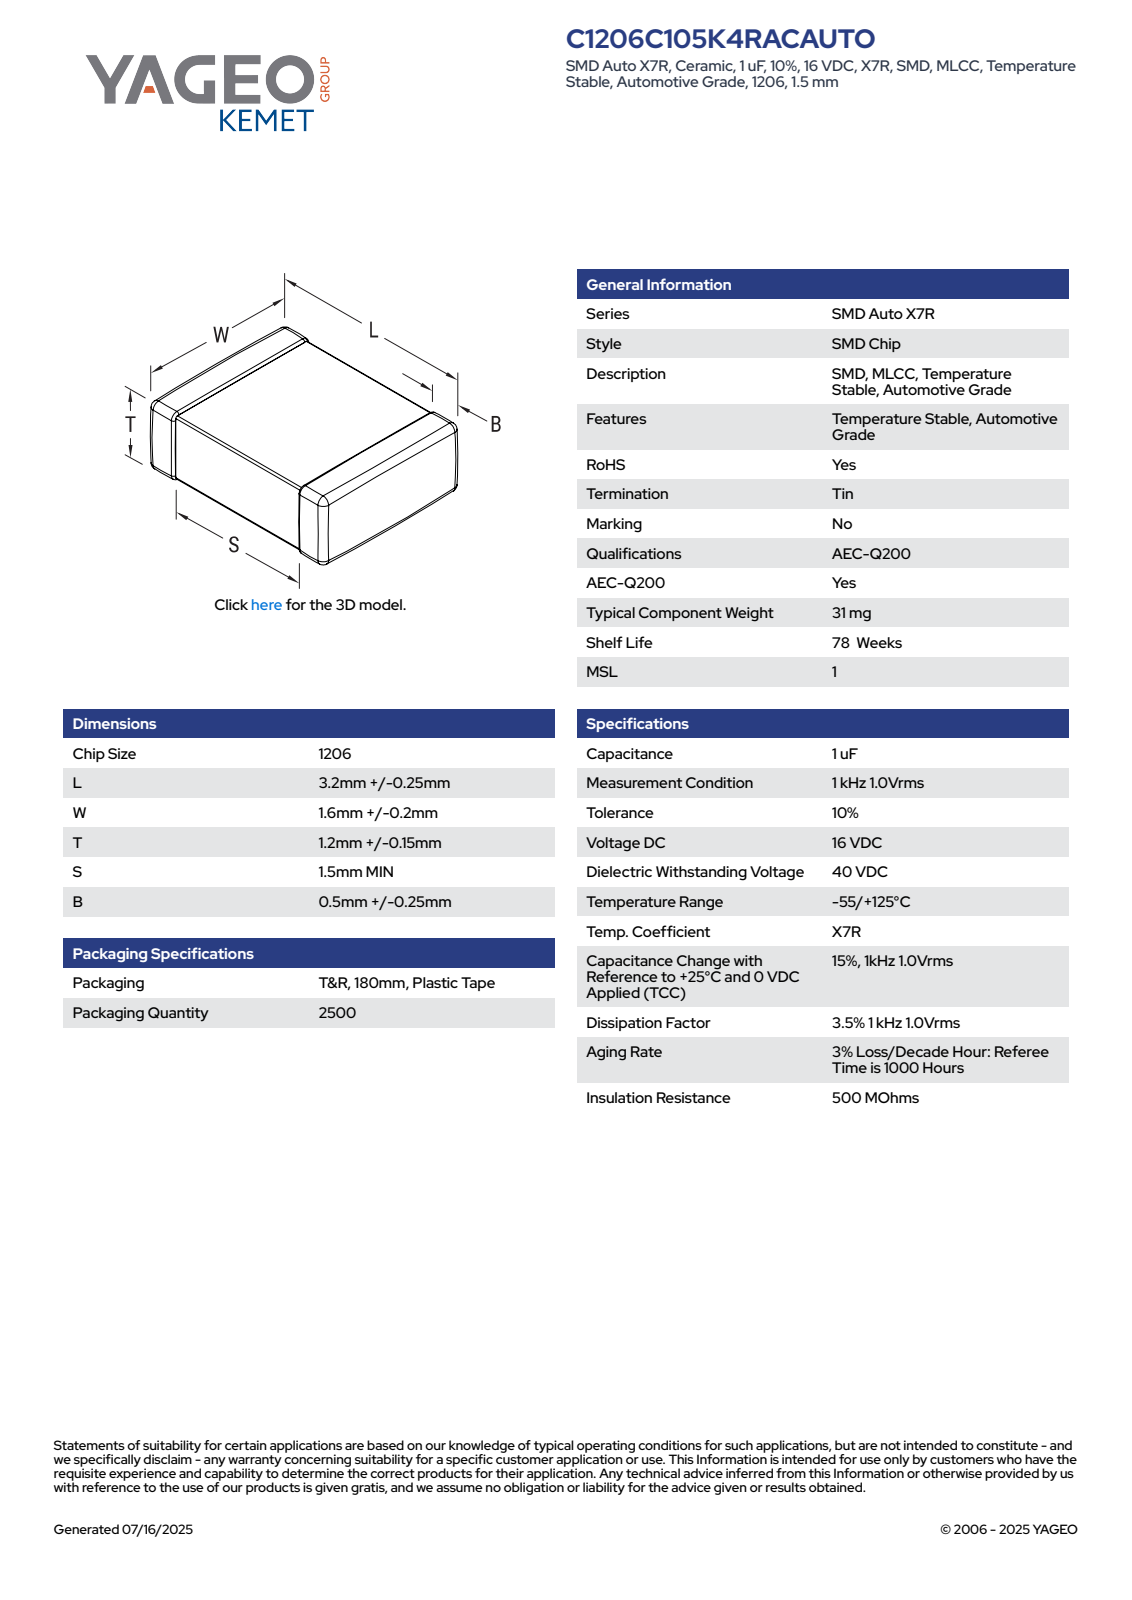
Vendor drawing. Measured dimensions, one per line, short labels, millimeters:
name: CCS_CCSTD_1206_L3.45W1.8T1.35B0.5
written by: SolidWorks 2021 (AUTOMOTIVE_DESIGN)
unit: mm
bodies: 4 solids, 125 faces (71 planar, 38 cylindrical, 16 other)
size: 3.45 × 1.8 × 1.35
volume: 8 mm³; area: 26 mm²
face distances: 1.31, 1.76, 1.27, 1.72, 1.35, 3.45, 1.8, 1.32, 1.28, 1.6
